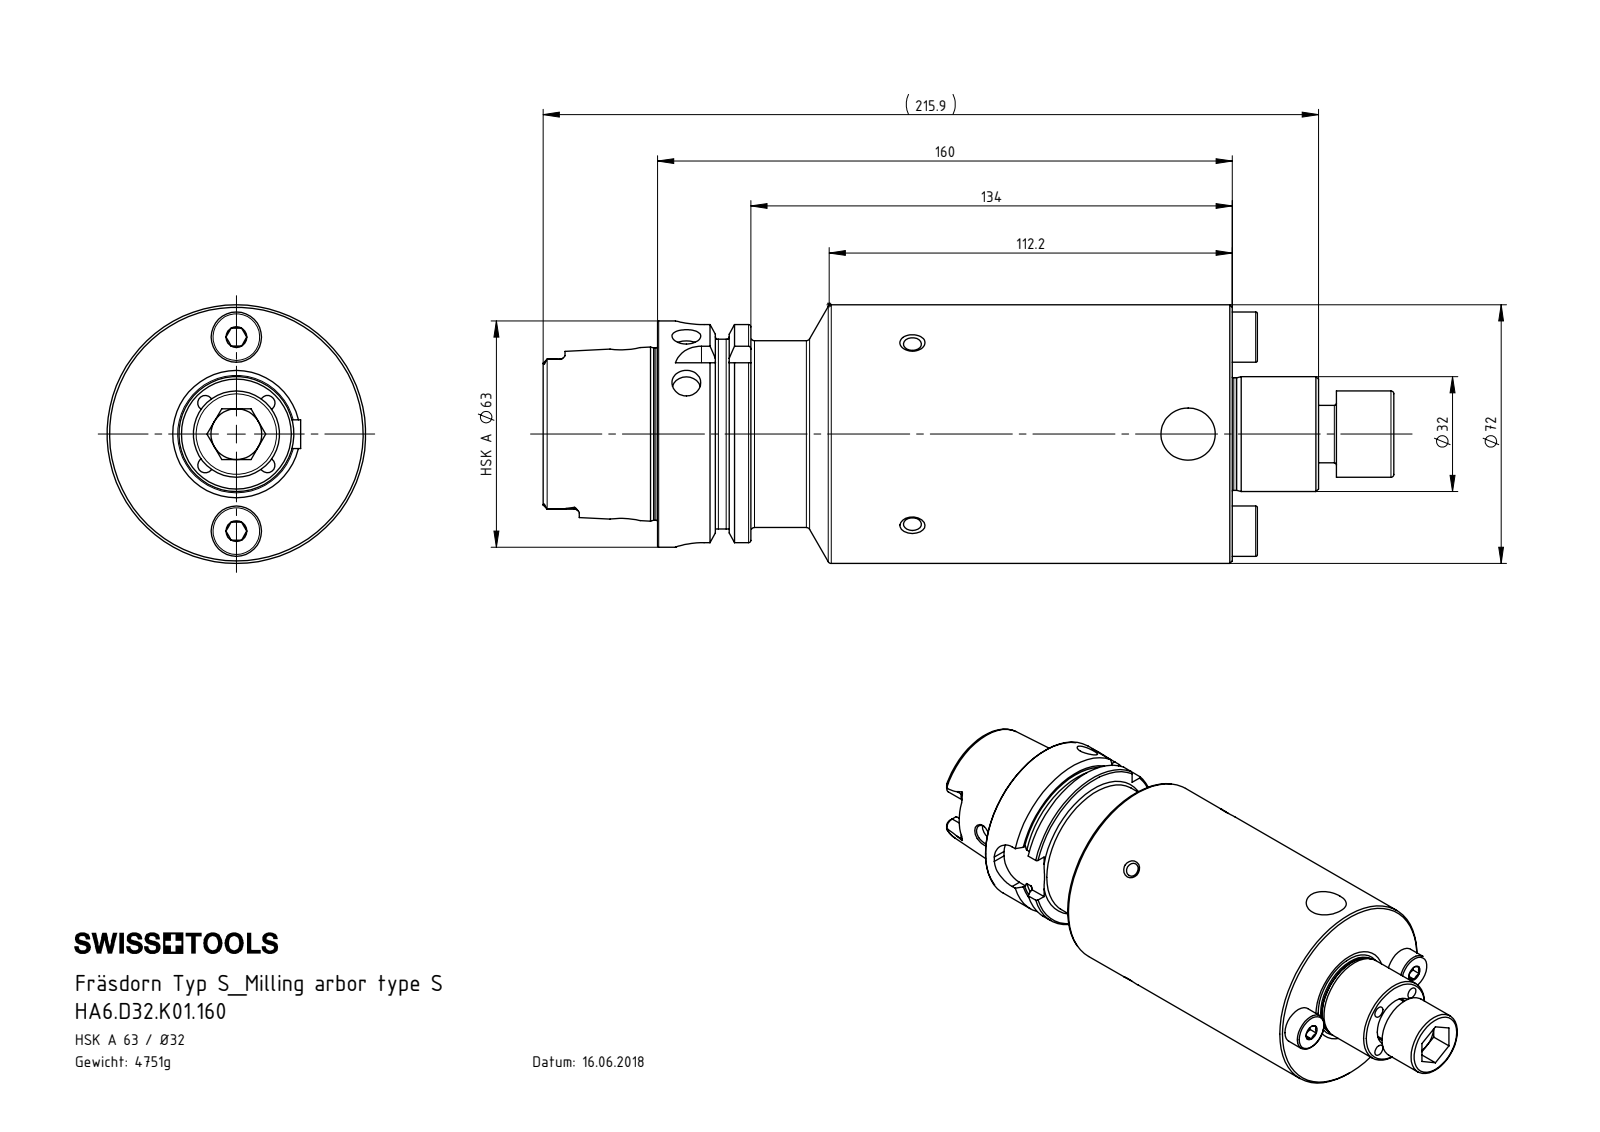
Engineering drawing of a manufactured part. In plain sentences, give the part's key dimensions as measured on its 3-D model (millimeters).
The part is named "DIN 6885 - 8x7x16; HA6-D32.K01.160_D_Fertigbearbeitung; D32-ER1.002.035_A; D32-ER2.001.022_B (+1 more)". Its 3-D file was written by "SolidWorks 2017 (AUTOMOTIVE_DESIGN)". It is 4 solids with 116 faces: 39 planar, 25 cylindrical and 52 other. Overall it measures 156.65 by 72 by 72 millimeters. Its volume is 16 805 cubic millimeters and its surface area 31 431 square millimeters. Round bosses or shafts: 2 of diameter 14, 2 of diameter 12, 2 of diameter 6, 2 of diameter 4.6, 1 of diameter 72, 1 of diameter 24, 1 of diameter 16. Partial cylindrical surfaces (rounded edges, fillets, slot ends): 2 of radius 4. The main face-to-face distances are 22, 16, 38, 14.14, 7, 5, 13, 35, 51, 1.
